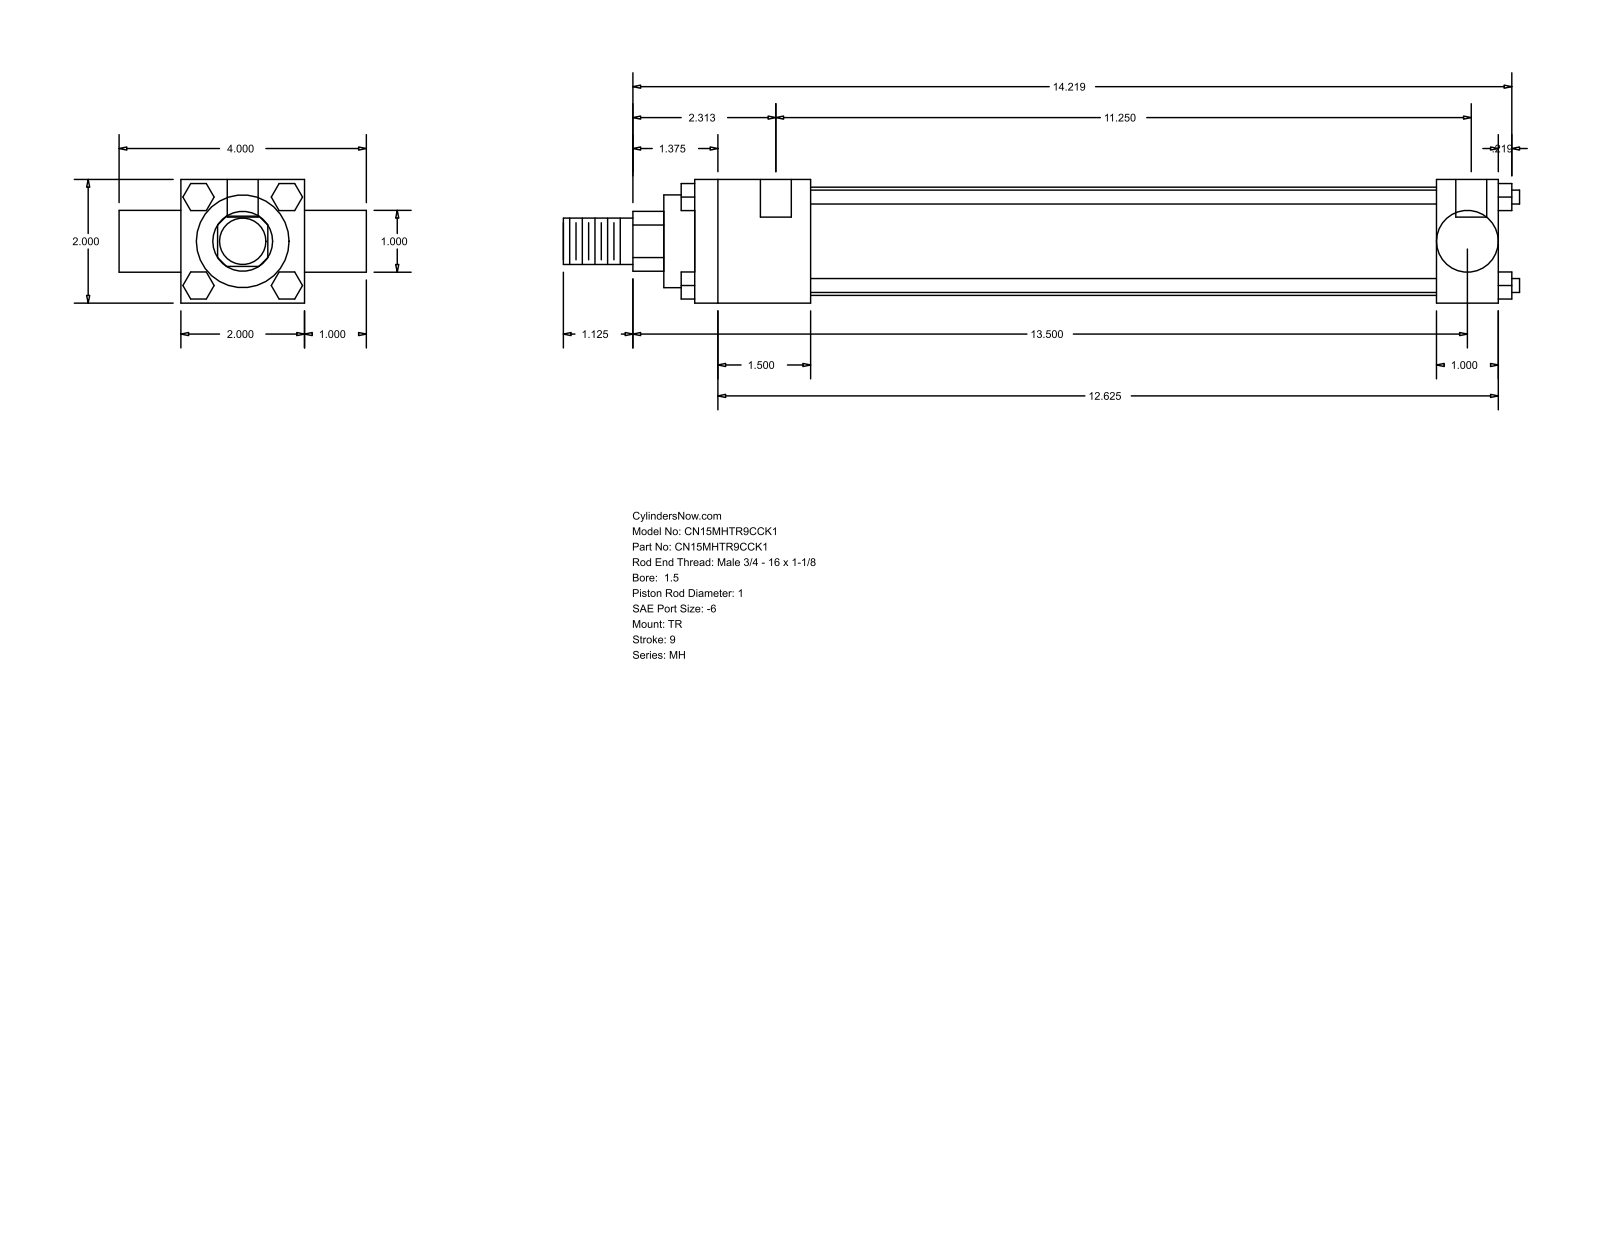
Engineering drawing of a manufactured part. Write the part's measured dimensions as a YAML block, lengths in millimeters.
part_name: "MH_TR__0150_1"
step_written_by: "GSSL Pune (CONFIG_CONTROL_DESIGN)"
units: millimeters
bodies: {solids: 0, faces: 120, planar: 92, cylindrical: 28, other: 0}
overall_size: [392.91, 101.6, 50.8]
round_holes:
  - {diameter: 5.56, count: 3}
  - {diameter: 12.7, count: 2}
round_bosses_or_shafts:
  - {diameter: 5.71, count: 4}
  - {diameter: 44.45, count: 1}
  - {diameter: 38.1, count: 1}
  - {diameter: 25.4, count: 1}
  - {diameter: 25.35, count: 1}
  - {diameter: 19.05, count: 1}
partial_cylinders:
  - {radius: 12.29, count: 1}
face_to_face_distances: [50.8, 25.4, 330.2, 76.2, 47.63, 282.57, 304.8, 257.17, 101.6, 12.7]
hole_center_spacings: [3.18, 285.75, 288.93]
